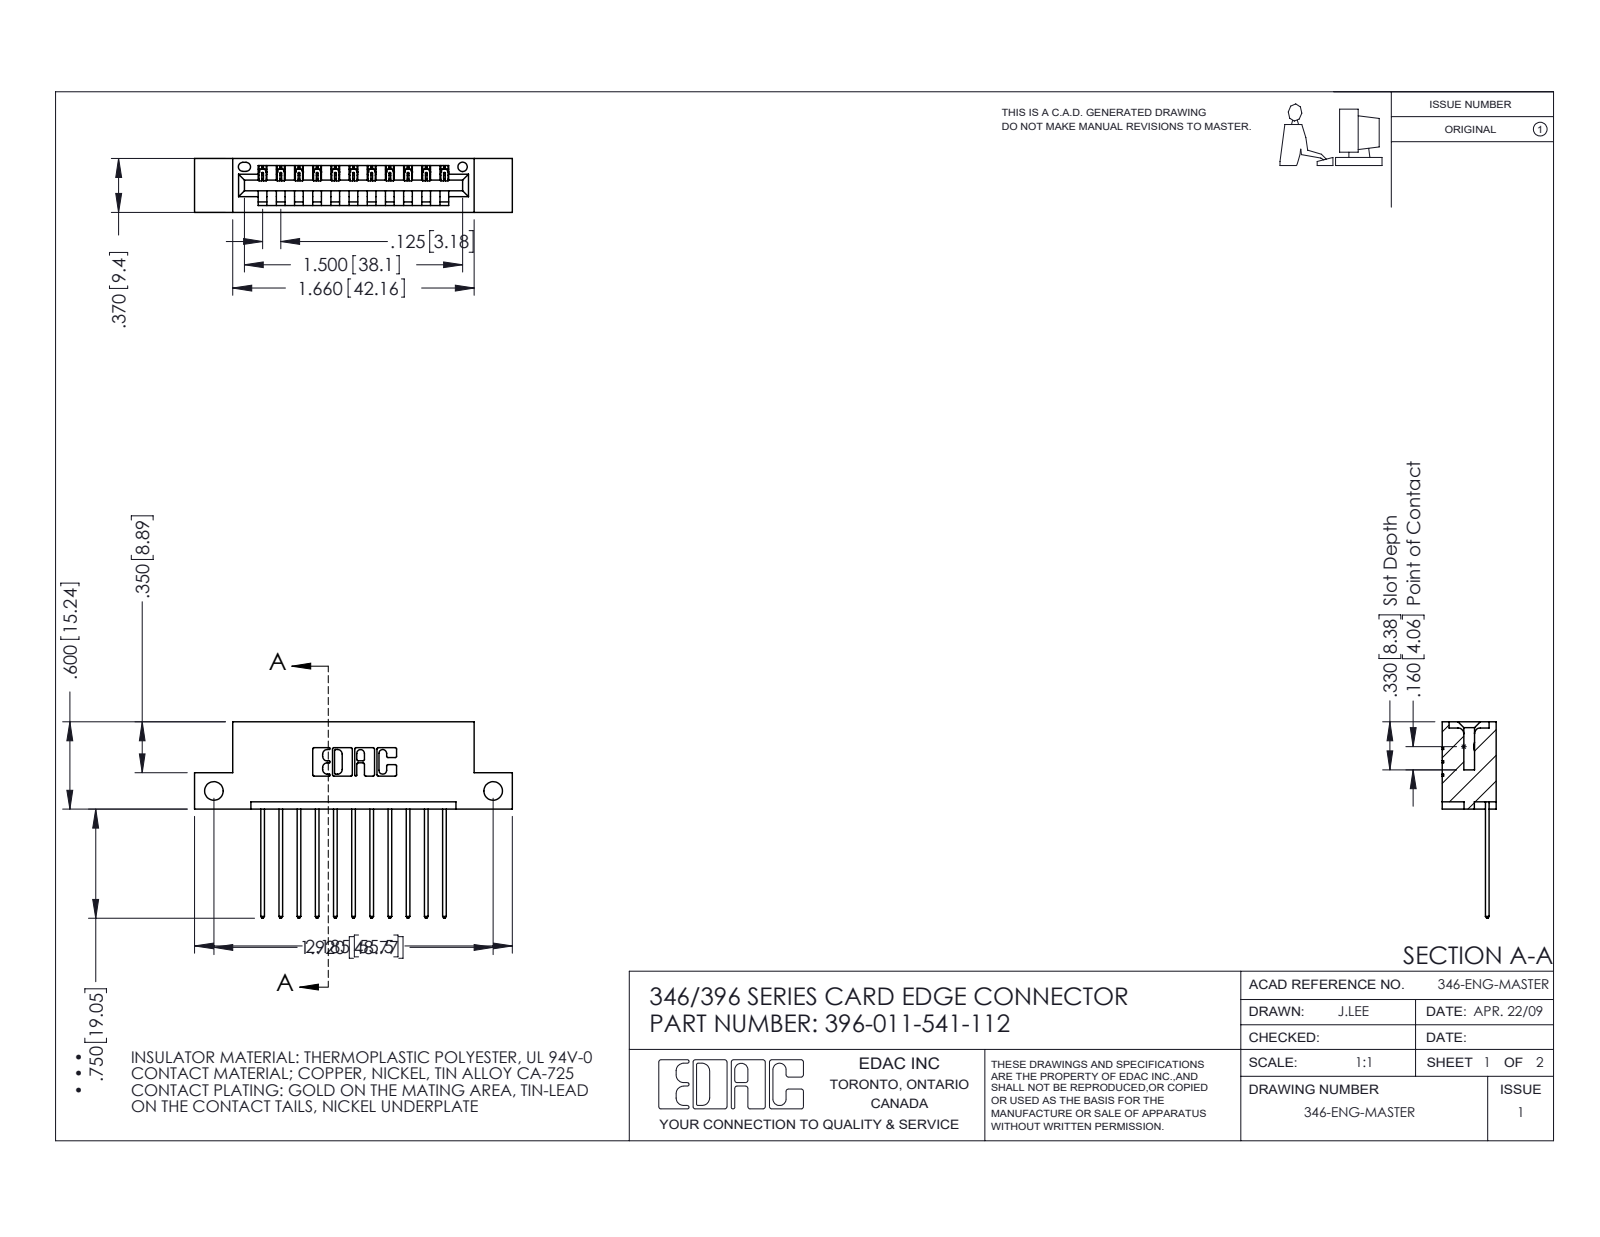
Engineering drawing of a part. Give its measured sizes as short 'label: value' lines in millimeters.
name: 396-011-541-112; 345-292-001_345-293-141; 346 Part_Flush Mounting Lugs - Side Mount
written by: SolidWorks 2016 (CONFIG_CONTROL_DESIGN)
unit: mm
bodies: 12 solids, 760 faces (516 planar, 244 cylindrical, 0 other)
size: 55.5 × 34.3 × 9.4
volume: 5 050 mm³; area: 6 046 mm²
holes: 2× ⌀3.3, 1× ⌀1.6
rounds: 22× R0.2, 22× R0.3, 22× R0.3, 6× R0.2, 6× R0.8, 3× R0.7, 2× R0.8, 2× R1
face distances: 6.4, 1.2, 8.2, 9.4, 1.8, 7.6, 0.6, 3.8, 5.6, 2.5
hole spacings: 48.8
